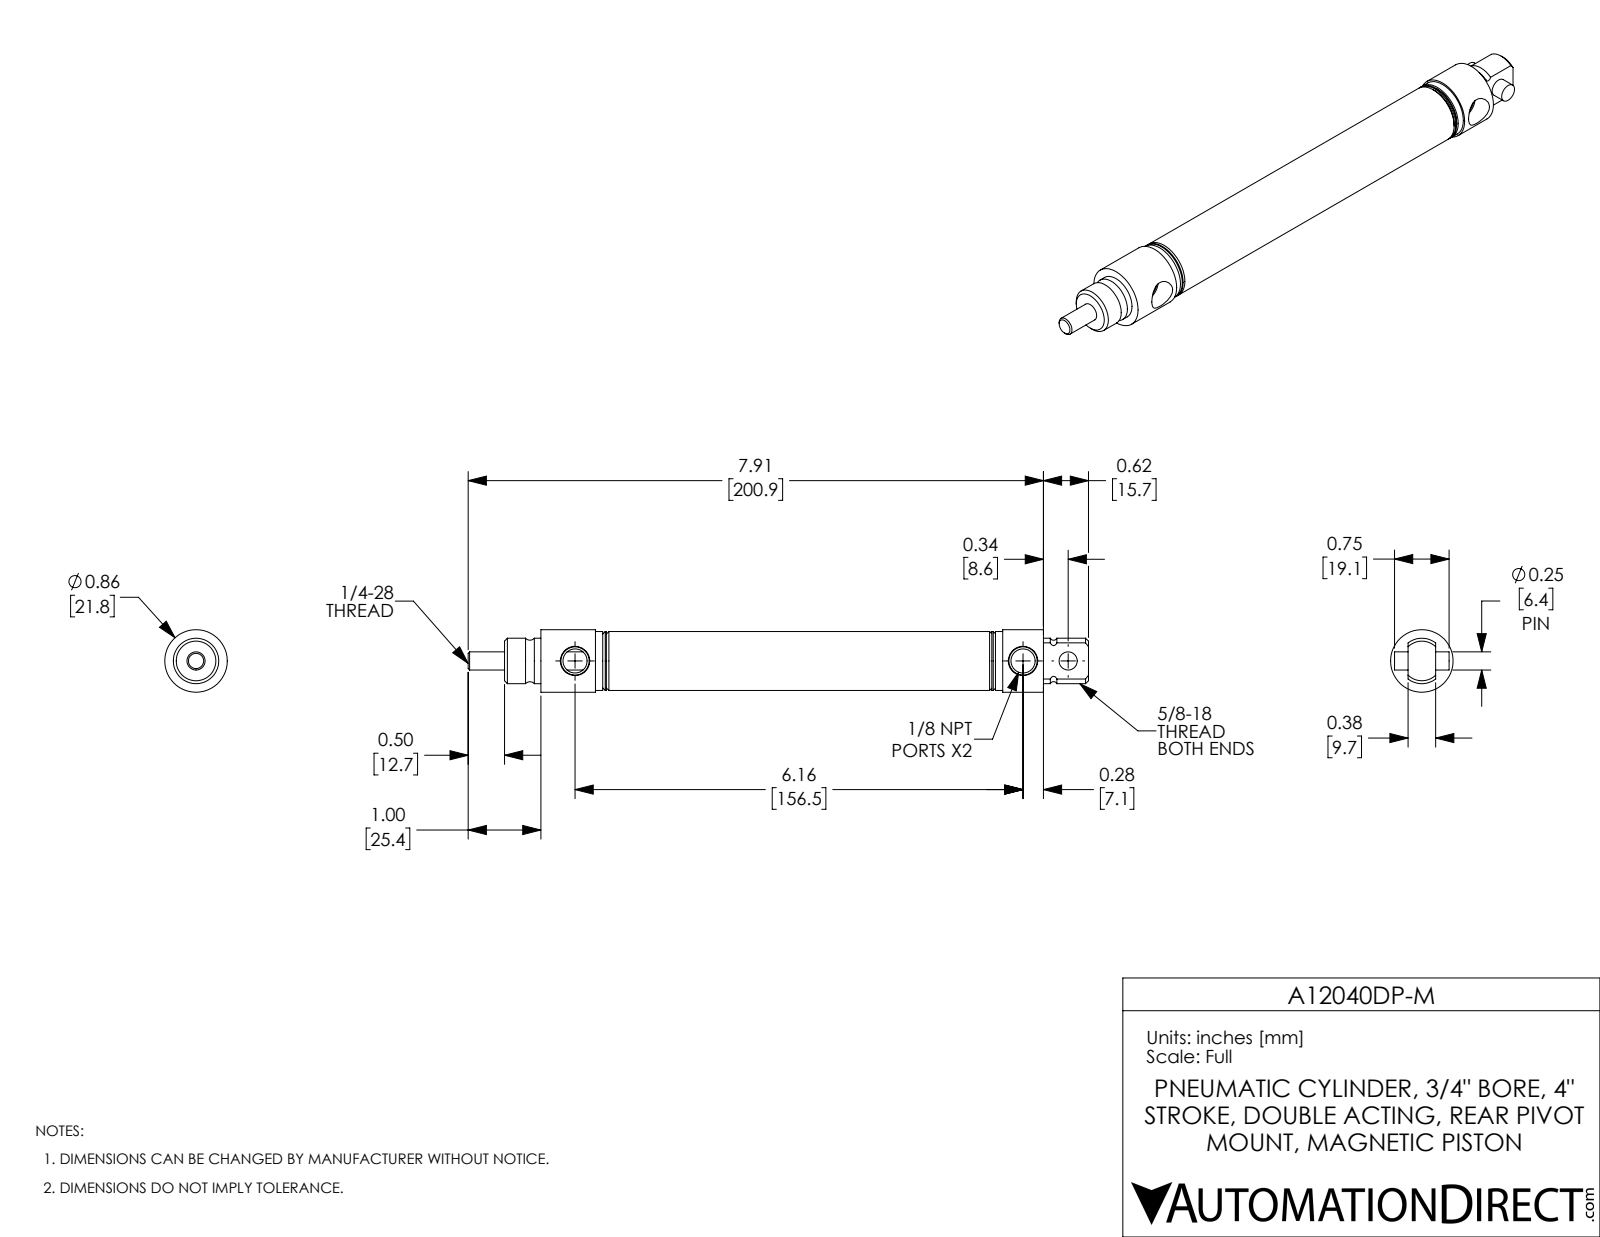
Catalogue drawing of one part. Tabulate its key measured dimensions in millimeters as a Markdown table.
| quantity | value |
| --- | --- |
| part name | A12040DP-M; A12040DP-M-PIN; A12040DP-M-Rod; A12040DP-M-MainBody |
| STEP written by | SolidWorks 2017 (AUTOMOTIVE_DESIGN) |
| units | millimeters |
| bodies | 3 solids, 91 faces (21 planar, 38 cylindrical, 32 other) |
| overall size | 216.7 × 21.8 × 21.8 |
| volume | 37 790 mm³ |
| surface area | 27 640 mm² |
| round holes (diameter × count) | 6.4 × 2, 8.4 × 2, 19.1 × 1 |
| round bosses / shafts (diameter × count) | 21.8 × 1, 20.6 × 1, 15.9 × 1 |
| main face-to-face distances | 12.7, 144.9, 114.3, 101.6, 30.6, 43.3, 144.9, 175.5, 132.2, 30.6 |
| hole center spacings | 15.7, 156.5, 172.2 |
